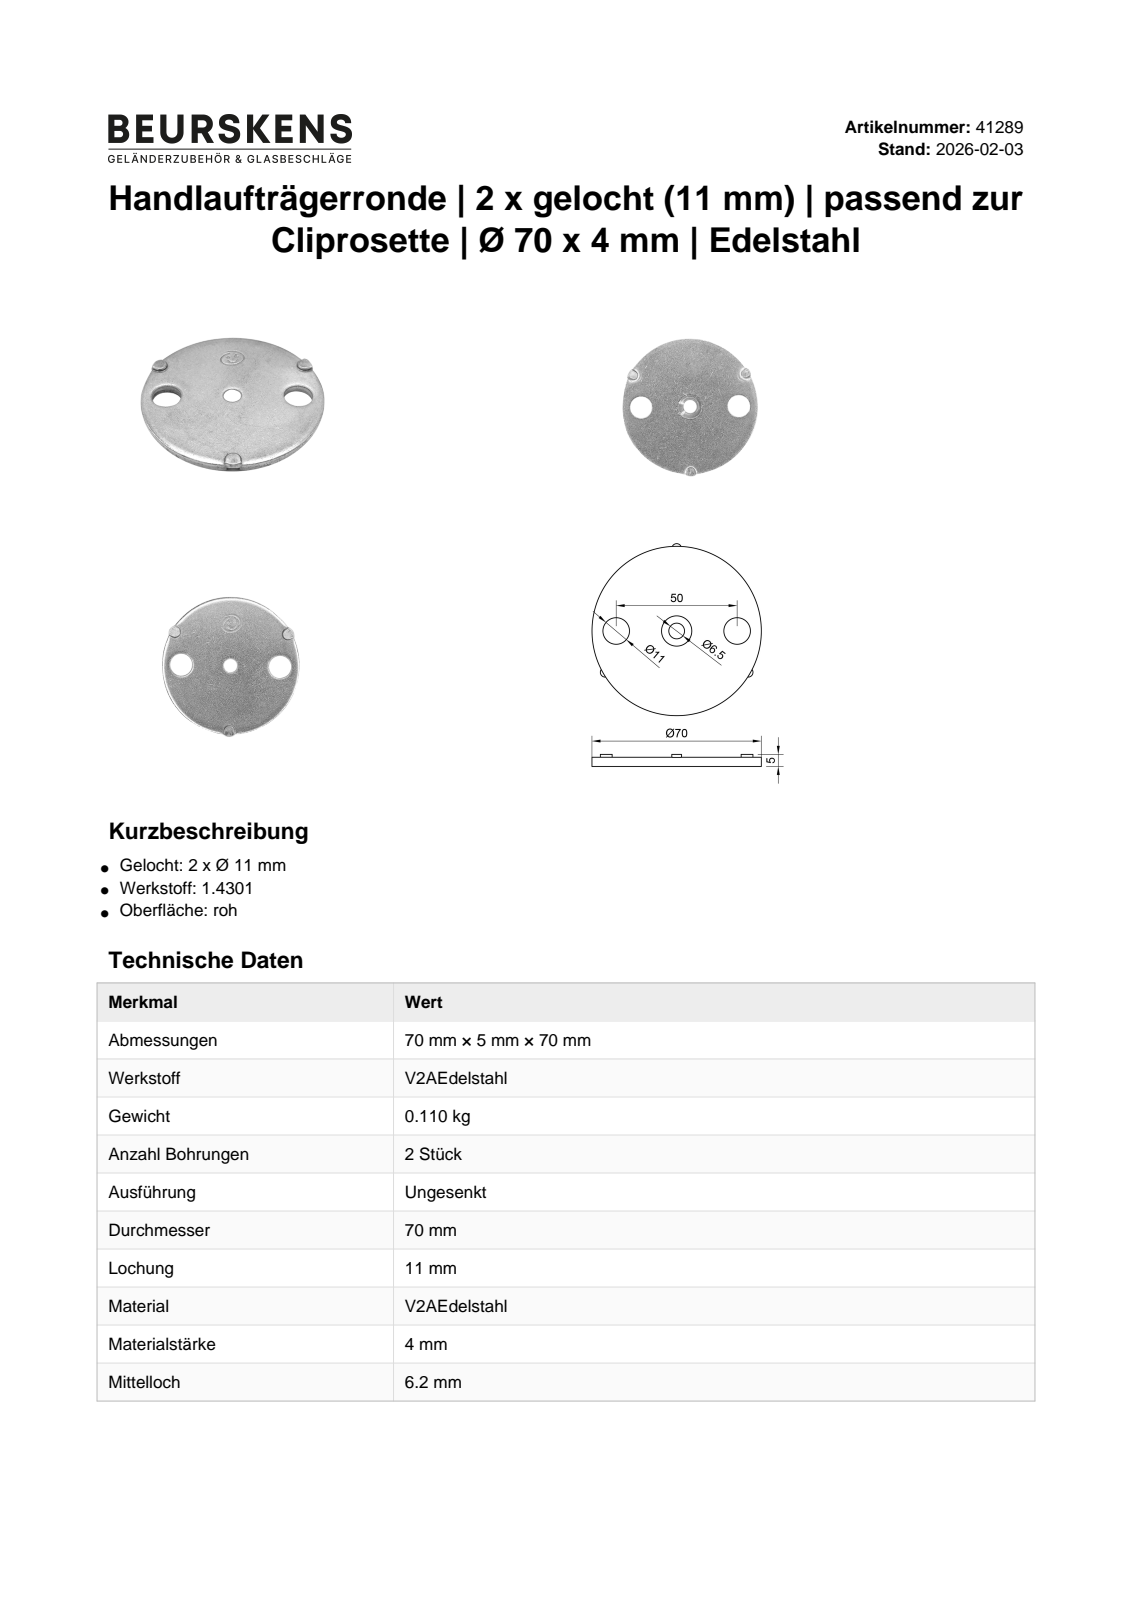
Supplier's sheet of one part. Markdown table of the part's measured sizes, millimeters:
| quantity | value |
| --- | --- |
| part name | 41289 |
| STEP written by | Autodesk Inventor 2022 (AUTOMOTIVE_DESIGN) |
| units | millimeters |
| bodies | 1 solid, 25 faces (14 planar, 10 cylindrical, 1 other) |
| overall size | 71.1 × 70 × 5 |
| volume | 13 716 mm³ |
| surface area | 8 472 mm² |
| round holes (diameter × count) | 11 × 2, 6.5 × 1 |
| round bosses / shafts (diameter × count) | 70 × 1 |
| partial cylindrical surfaces (radius × count) | 2 × 6 |
| main face-to-face distances | 3.8, 5, 1.2, 3.75, 1.25, 4 |
| hole center spacings | 25, 50 |
